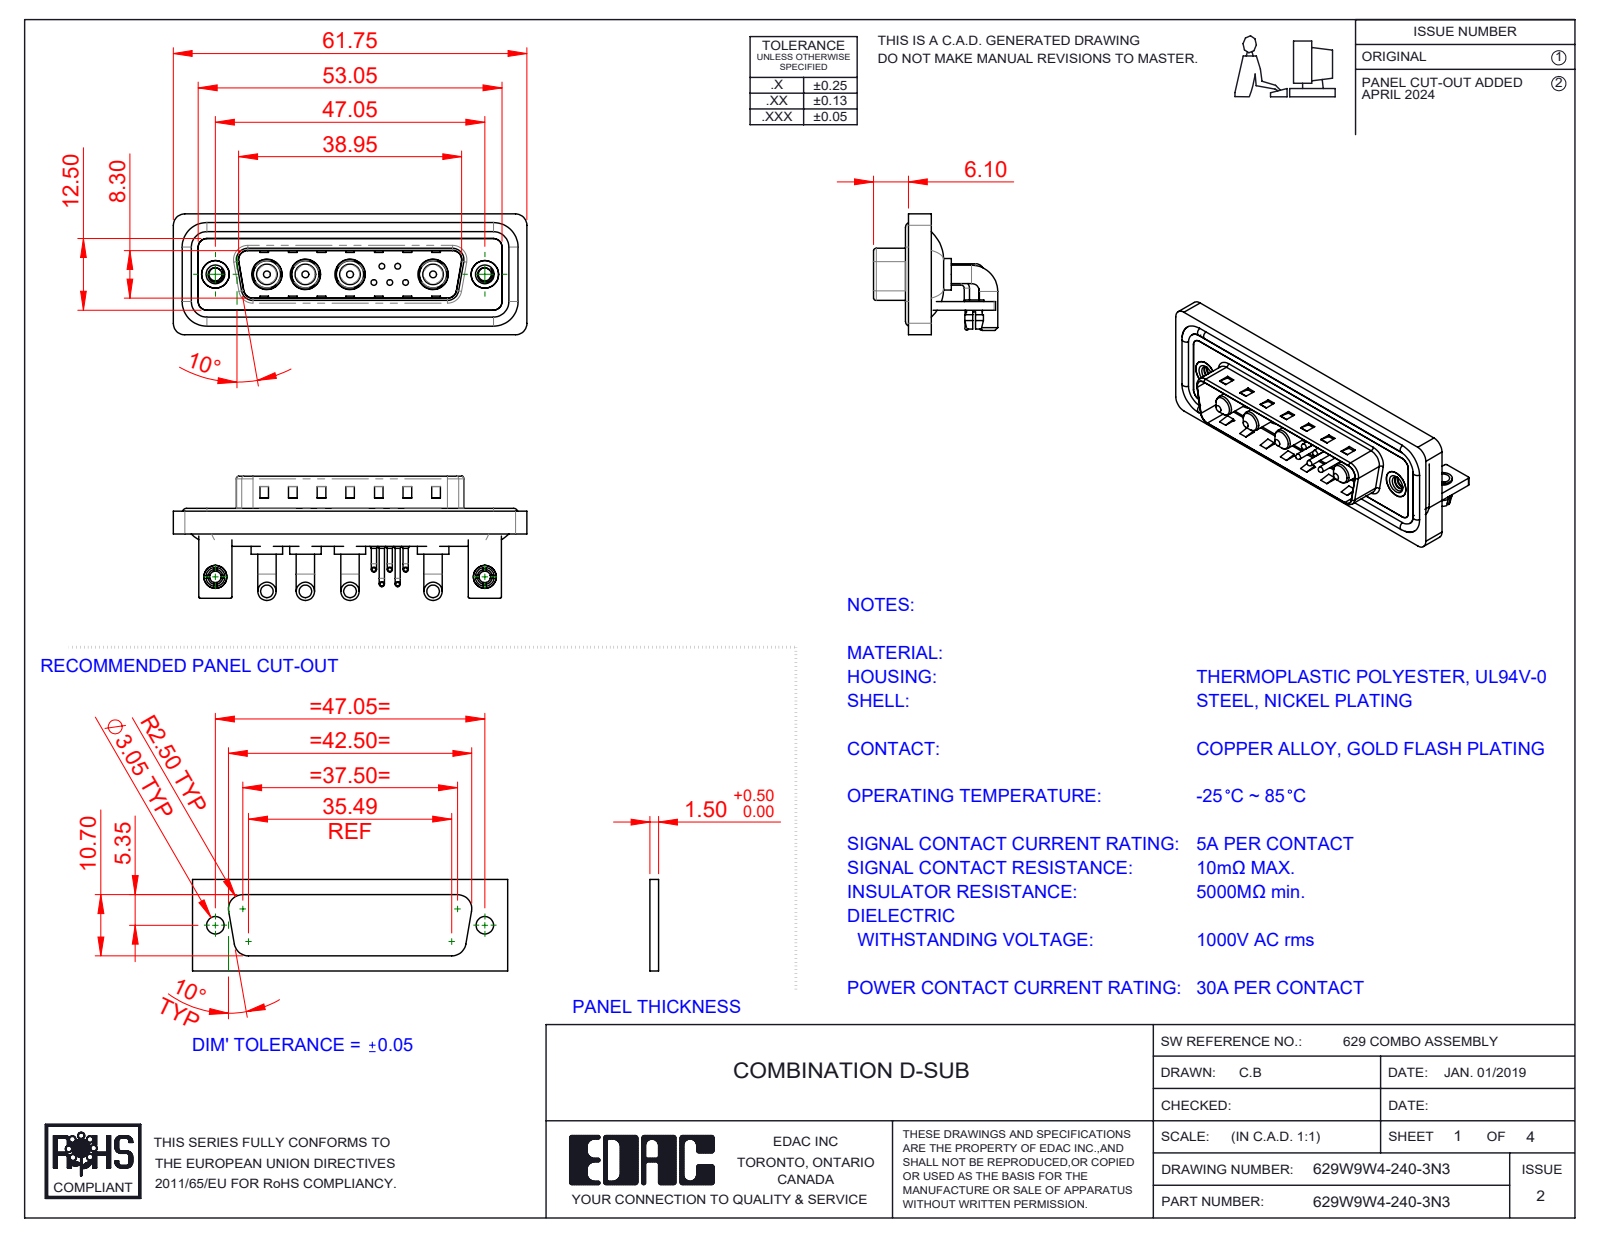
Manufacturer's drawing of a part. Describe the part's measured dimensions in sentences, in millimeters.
The part is named "629Combo Threaded Rivet_3; 629Combo Waterproof Housing_25 Contacts; 629Combo Contact Row 2; 629Combo Shell Rear_25 Contacts (+7 more)". Its 3-D file was written by "SolidWorks 2023 (CONFIG_CONTROL_DESIGN)". It is 24 solids with 1337 faces: 637 planar, 502 cylindrical and 198 other. Overall it measures 61.75 by 21.7 by 21.1 millimeters. Its volume is 8 130 cubic millimeters and its surface area 13 248 square millimeters. Round holes: 7 of diameter 2, 5 of diameter 0.75, 5 of diameter 1.6, 4 of diameter 4.85, 4 of diameter 5.3, 2 of diameter 2.26, 2 of diameter 2.5, 2 of diameter 3.2, 2 of diameter 4, 2 of diameter 4.8, 2 of diameter 5. Round bosses or shafts: 10 of diameter 0.9, 8 of diameter 3.2, 5 of diameter 1.5, 5 of diameter 1, 5 of diameter 0.65, 4 of diameter 5.5, 4 of diameter 5.2, 4 of diameter 4.75. Partial cylindrical surfaces (rounded edges, fillets, slot ends): 19 of radius 2, 18 of radius 1.5, 16 of radius 0.25, 9 of radius 0.5, 8 of radius 1.6, 5 of radius 1.01, 4 of radius 0.6, 4 of radius 0.65. The main face-to-face distances are 0.4, 1.5, 0.8, 2.9, 2.1, 1.1, 3.7, 4.1, 4.5, 1.6. The hole center spacings are 3.16, 2.77, 5.04, 14.5, 47.05, 2.78, 4.4, 4.41.
